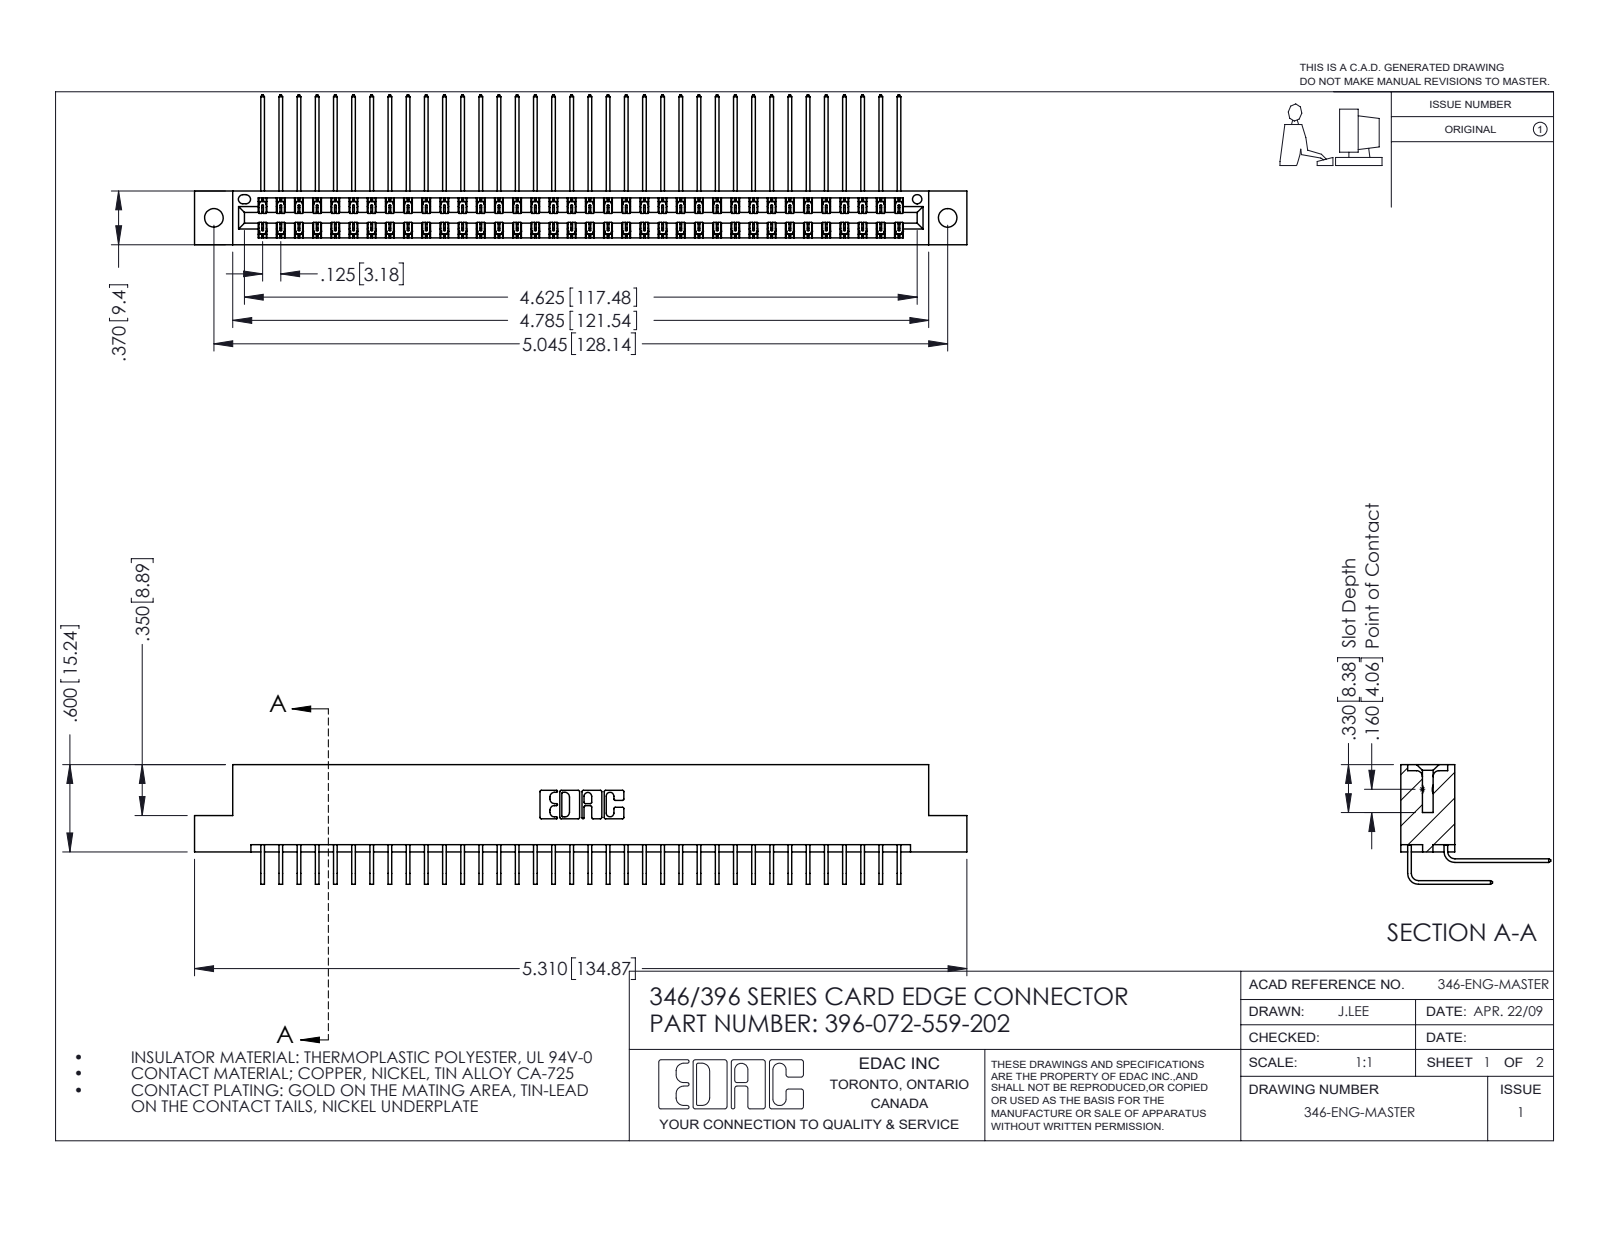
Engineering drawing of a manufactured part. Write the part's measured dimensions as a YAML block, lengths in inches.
part_name: "345-292-001_559 Tail - 2; 345-292-001_558 559 Tail - 1; 396-072-559-202; 346 Part_Flush Mounting Lugs - 0.128 Dia"
step_written_by: "SolidWorks 2016 (CONFIG_CONTROL_DESIGN)"
units: inches
bodies: {solids: 73, faces: 4010, planar: 2740, cylindrical: 1270, other: 0}
overall_size: [5.31, 1.03, 0.823]
volume: 0.823
surface_area: 31.25
round_holes:
  - {diameter: 0.128, count: 2}
  - {diameter: 0.064, count: 1}
partial_cylinders:
  - {radius: 0.006, count: 108}
  - {radius: 0.01, count: 22}
  - {radius: 0.007, count: 6}
  - {radius: 0.031, count: 6}
  - {radius: 0.026, count: 3}
  - {radius: 0.014, count: 2}
  - {radius: 0.022, count: 2}
  - {radius: 0.024, count: 2}
face_to_face_distances: [0.048, 0.322, 0.025, 0.37, 0.25, 0.072, 0.298, 0.275, 0.148, 0.222]
hole_center_spacings: [0.246, 4.836, 5.045]
